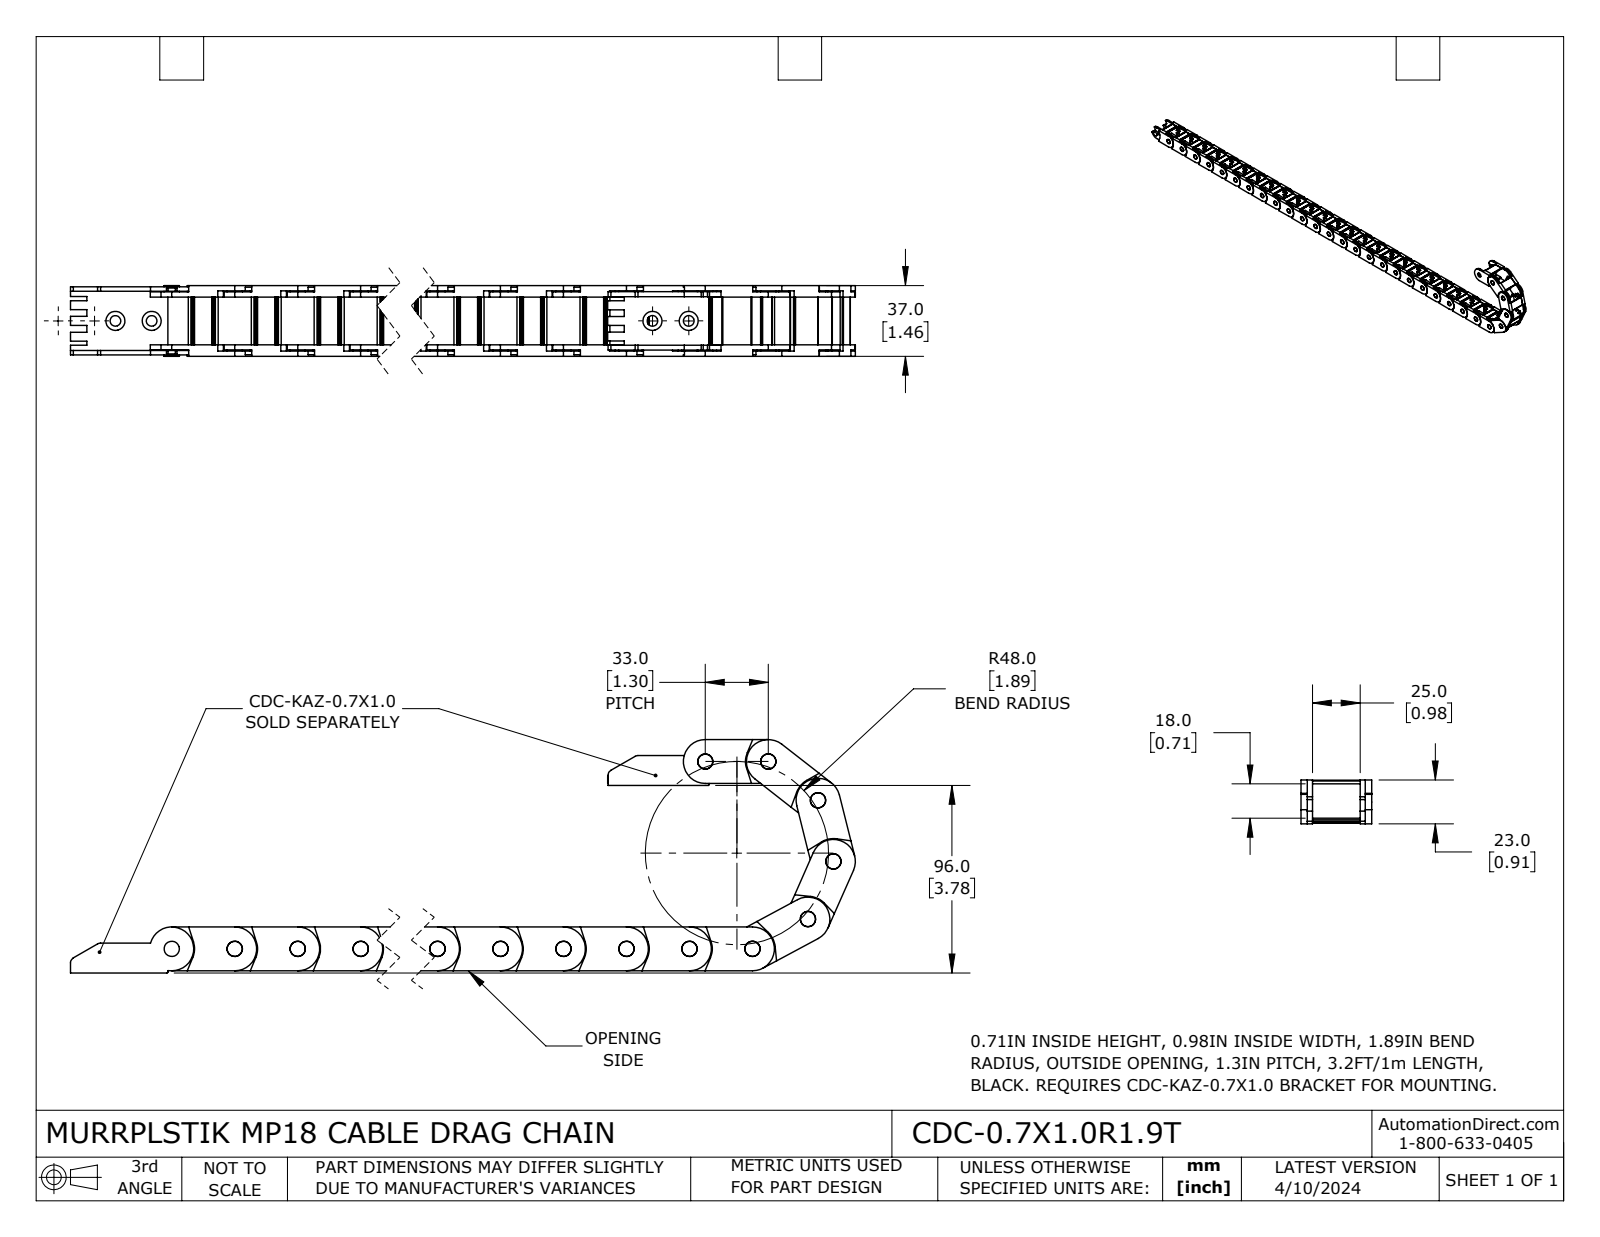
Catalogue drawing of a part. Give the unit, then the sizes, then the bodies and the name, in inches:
Units: inches
Overall size (bounding box): 35.042 × 4.767 × 1.457
Round holes (diameter × count): ⌀0.315 ×30
Round bosses / shafts (diameter × count): ⌀0.315 ×1
Partial cylindrical surfaces — rounded edges, fillets, slot ends (radius × count): R0.02 ×120, R0.059 ×120, R0.008 ×60, R0.012 ×60, R0.453 ×31, R0.47 ×31, R0.197 ×30, R0.215 ×30
Main face-to-face distances: 1.22, 0.106, 0.13, 0.236, 1.457, 1.327, 1.091, 0.984, 1.35, 0.024
Hole centre spacings: 1.299, 2.598, 3.898, 5.197, 6.496, 7.795, 9.094, 10.394
Volume: 16.69 in³ · Surface area: 339.5 in²
Bodies: 30 solids, 2490 faces (1290 planar, 1200 cylindrical, 0 other)
Part name (STEP PRODUCT): CDC-0.7X1.0R1.9T
STEP written by: SolidWorks 2023 (CONFIG_CONTROL_DESIGN)
